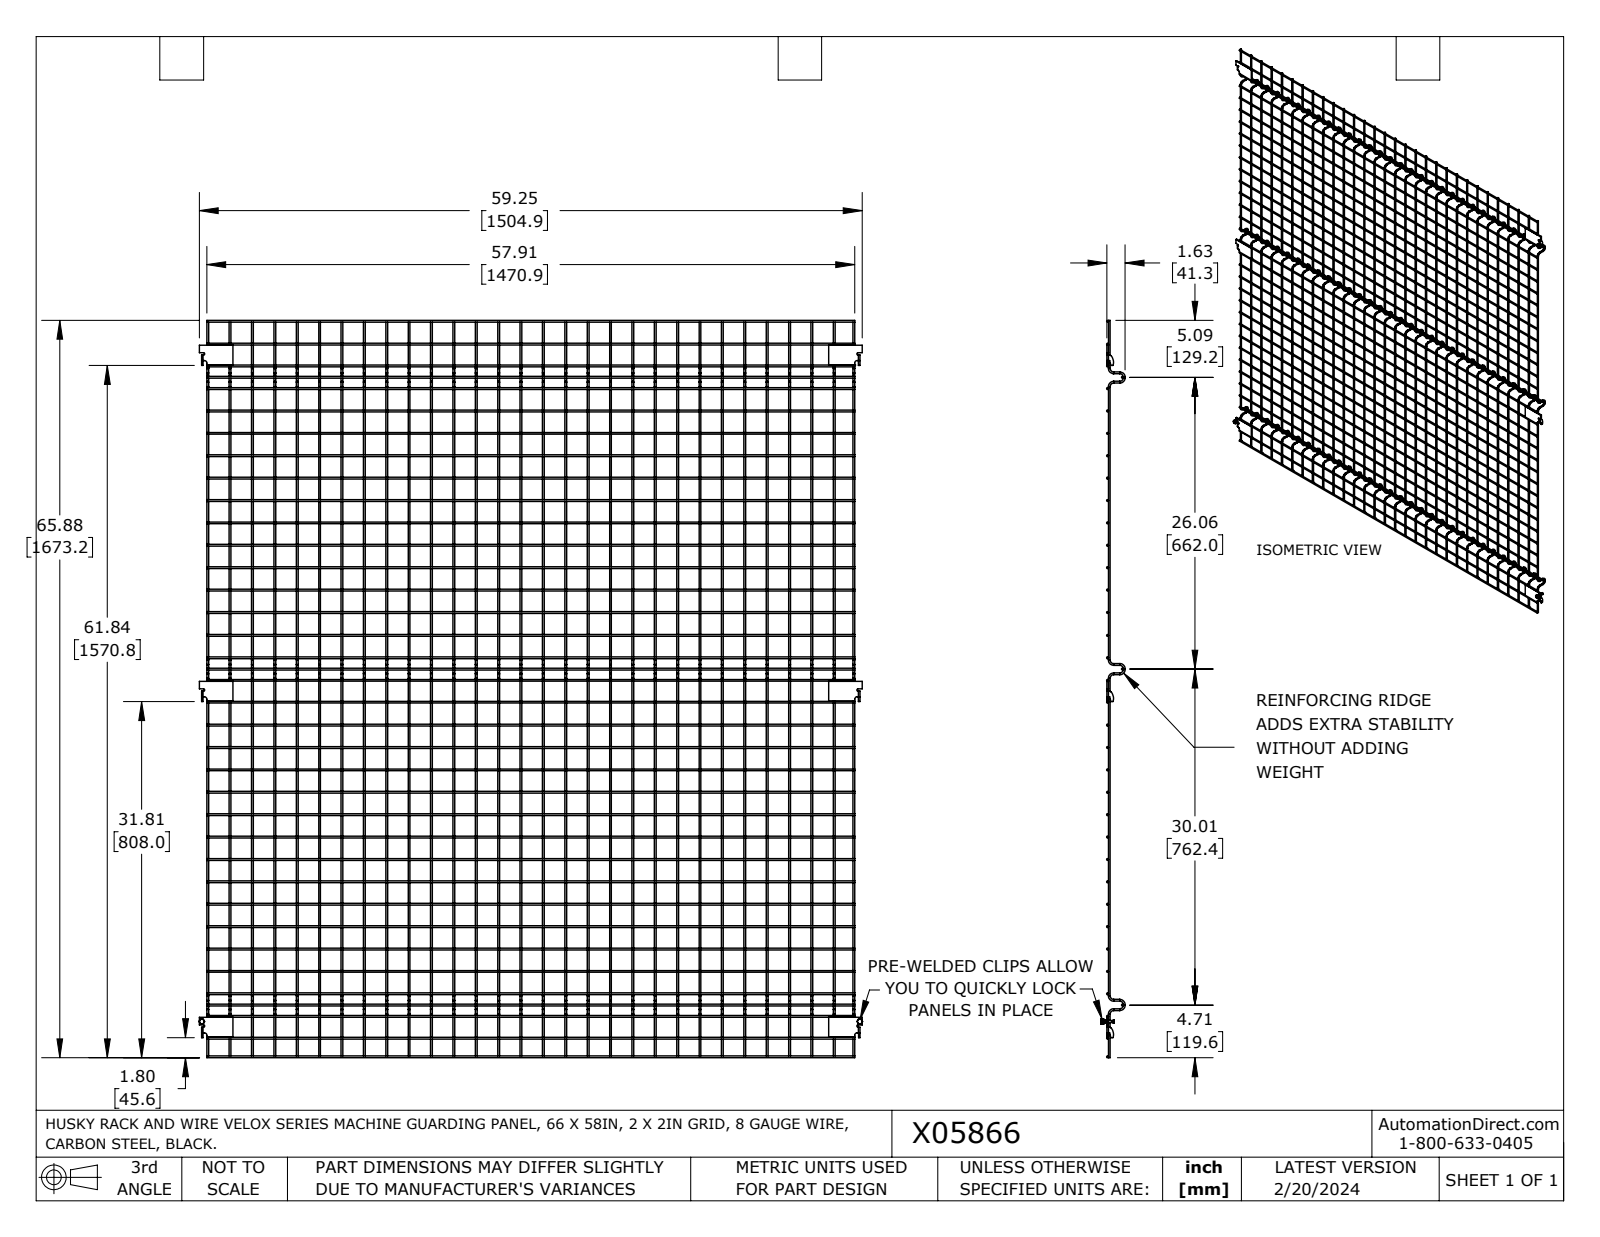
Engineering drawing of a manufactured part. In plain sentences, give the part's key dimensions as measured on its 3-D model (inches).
The part is named "X05866". Its 3-D file was written by "SolidWorks 2023 (AUTOMOTIVE_DESIGN)". It is 77 solids with 1101 faces: 242 planar, 475 cylindrical and 384 other. Overall it measures 65.875 by 59.313 by 2.103 inches. Its volume is 90.55 cubic inches and its surface area 2 237 square inches. Round holes: 2 of diameter 0.201, 2 of diameter 0.25. Round bosses or shafts: 277 of diameter 0.16, 2 of diameter 0.39, 2 of diameter 0.245, 2 of diameter 0.187. Partial cylindrical surfaces (rounded edges, fillets, slot ends): 6 of radius 0.1, 6 of radius 0.218, 3 of radius 0.25, 3 of radius 0.865, 2 of radius 0.009, 2 of radius 0.067, 2 of radius 0.134. The main face-to-face distances are 0.134, 0.125, 1.765, 30.031, 0.467, 58.377, 30.016, 60.047, 2.798, 56.046. The hole center spacings are 58.808.
